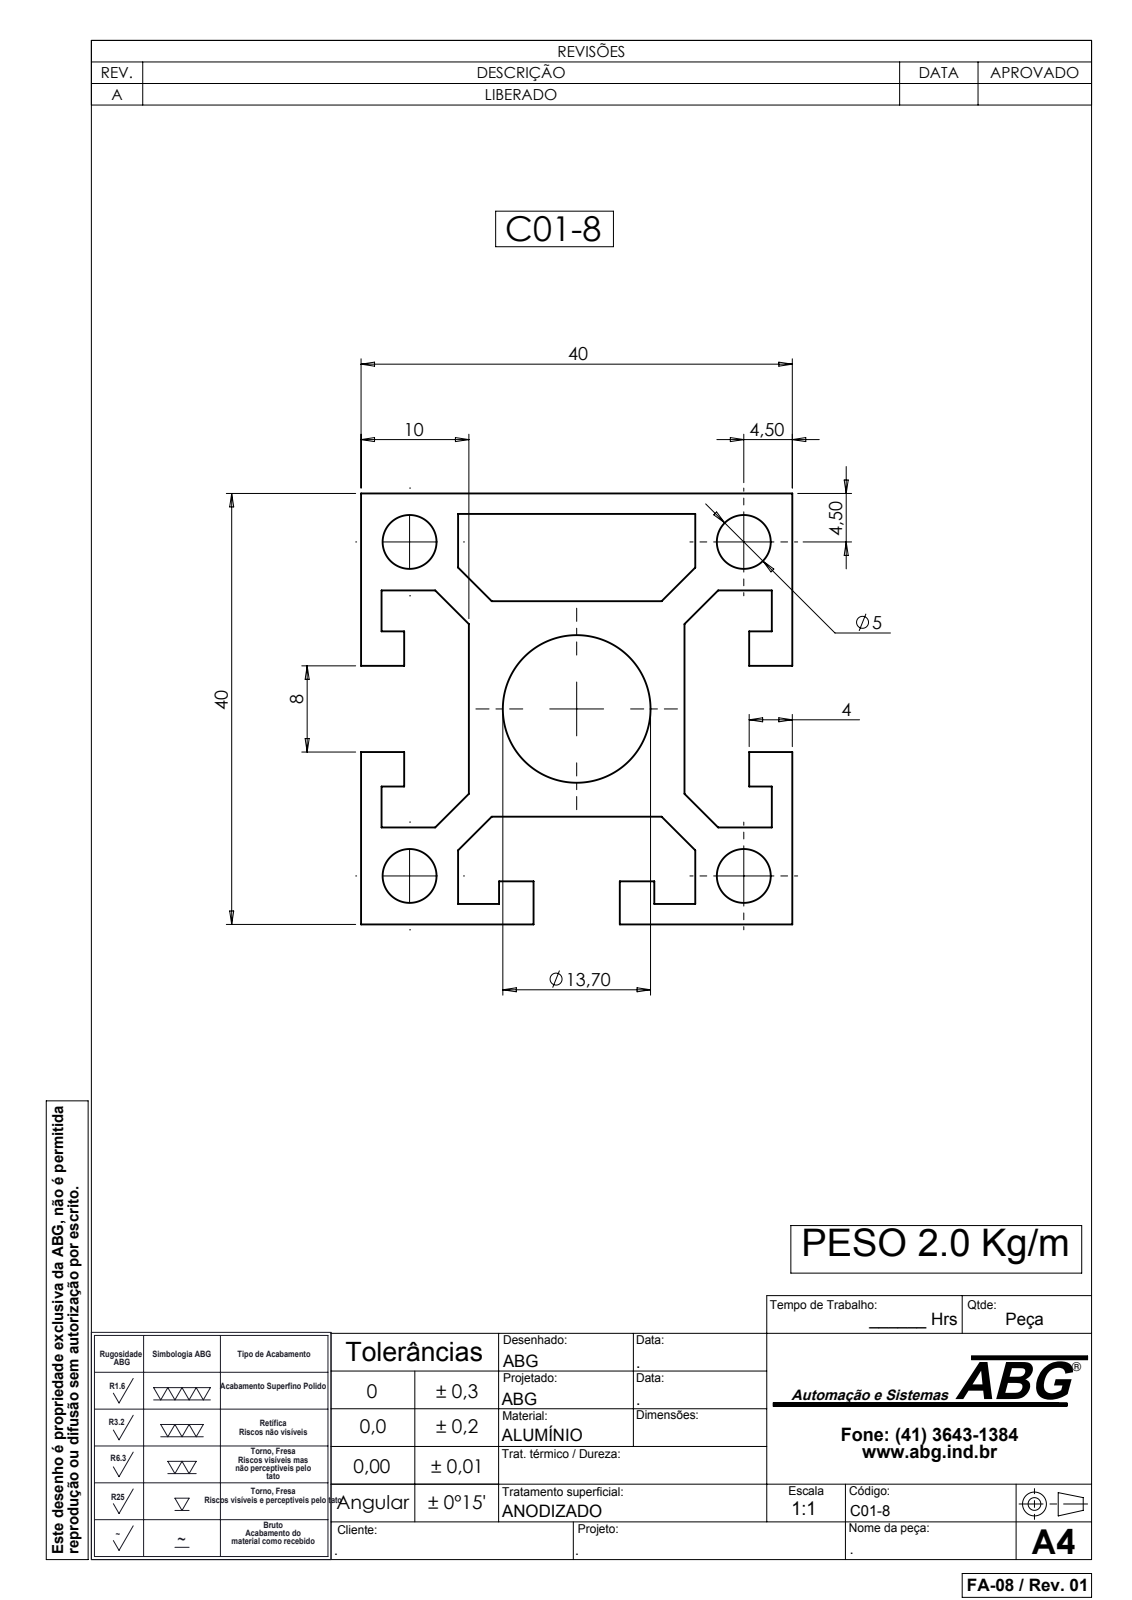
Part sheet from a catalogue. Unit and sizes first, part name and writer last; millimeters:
Units: millimetres
Overall size (bounding box): 6000 × 40 × 40
Round holes (diameter × count): ⌀5 ×4, ⌀13.7 ×1
Main face-to-face distances: 40, 30, 10, 20, 1.9, 38.1, 6, 9, 31, 1
Hole centre spacings: 21.92, 31, 43.84
Volume: 4 170 000 mm³ · Surface area: 2 885 000 mm²
Bodies: 1 solid, 64 faces (54 planar, 10 cylindrical, 0 other)
Part name (STEP PRODUCT): C01-8
STEP written by: SolidWorks 2007 (CONFIG_CONTROL_DESIGN)
